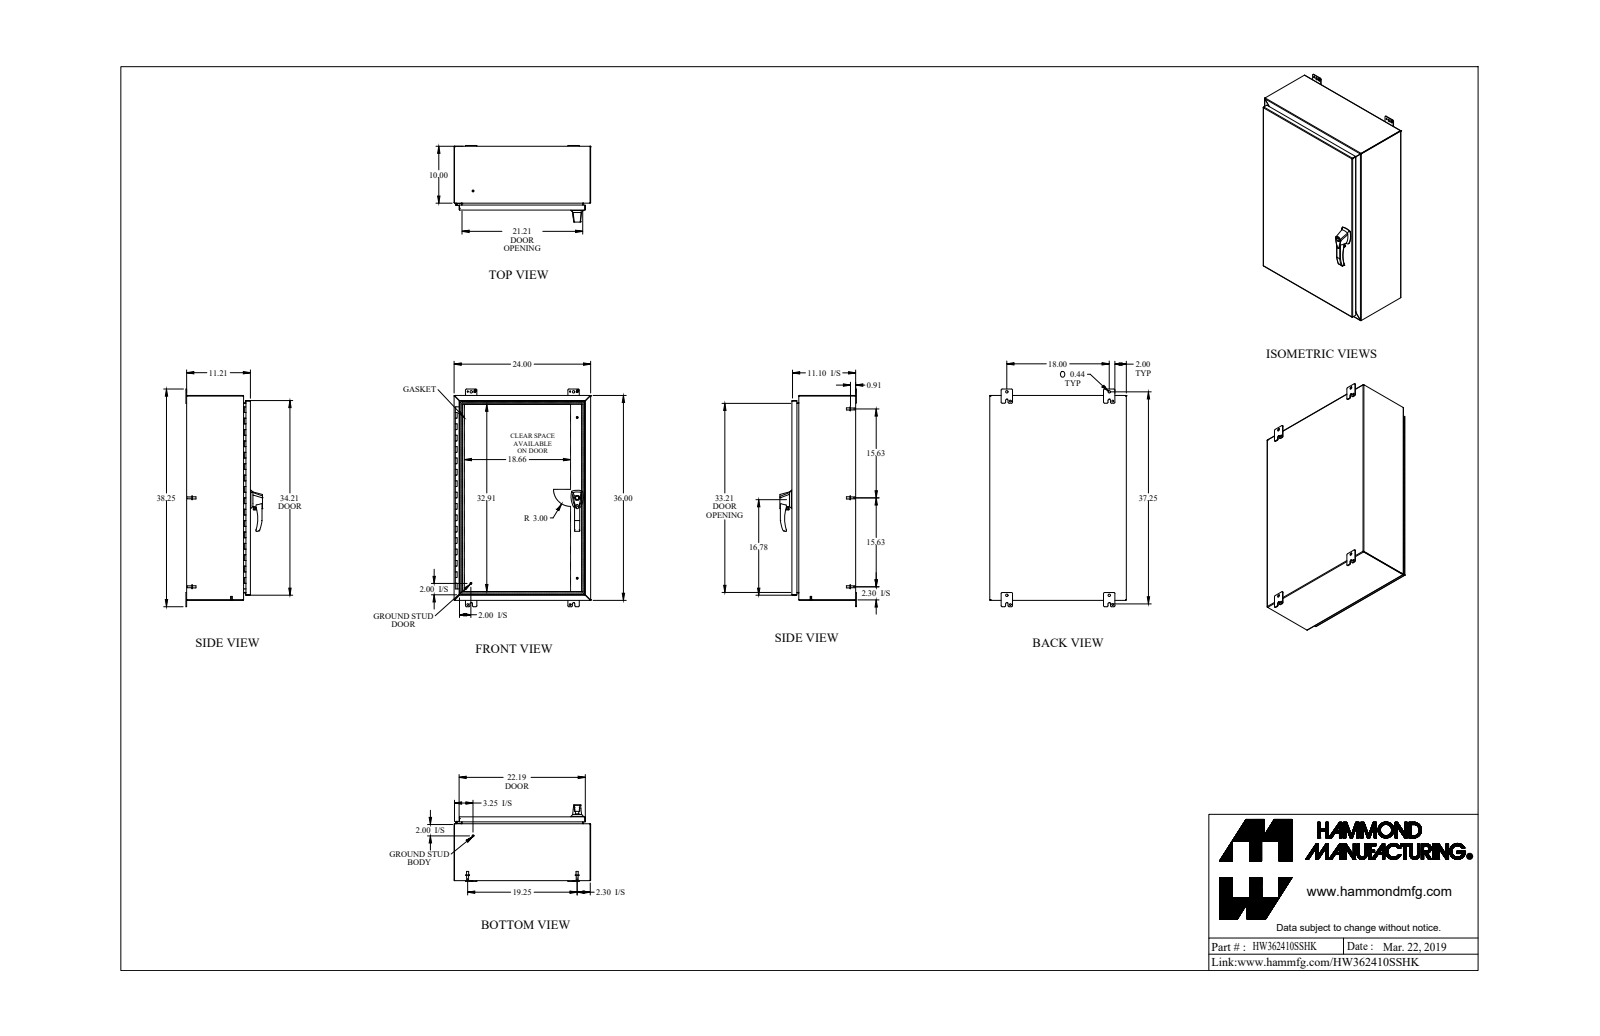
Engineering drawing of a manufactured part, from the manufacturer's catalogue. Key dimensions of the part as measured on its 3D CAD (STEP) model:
Part name (STEP PRODUCT): HW362410SSHK
STEP written by: SolidWorks 2018 (AUTOMOTIVE_DESIGN)
Units: inches
Bodies: 44 solids, 1544 faces (737 planar, 641 cylindrical, 166 other)
Overall size (bounding box): 38.25 × 24 × 13.45
Volume: 270.1 in³ · Surface area: 7 073 in²
Round holes (diameter × count): ⌀0.176 ×6, ⌀0.313 ×5, ⌀0.25 ×3, ⌀0.265 ×3, ⌀0.413 ×3, ⌀0.196 ×2, ⌀0.256 ×2, ⌀0.394 ×2, ⌀0.437 ×2, ⌀0.187 ×1, ⌀0.233 ×1, ⌀0.33 ×1
Round bosses / shafts (diameter × count): ⌀0.375 ×11, ⌀0.25 ×7, ⌀0.65 ×6, ⌀0.332 ×6, ⌀0.156 ×6, ⌀1 ×3, ⌀0.51 ×3, ⌀0.63 ×2
Partial cylindrical surfaces — rounded edges, fillets, slot ends (radius × count): R0.25 ×27, R0.188 ×23, R0.036 ×20, R0.108 ×20, R0.06 ×12, R0.125 ×9, R0.045 ×8, R0.218 ×8
Main face-to-face distances: 0.072, 11.138, 11.066, 0.072, 11.138, 11.21, 23.928, 35.928, 23.856, 24
Hole centre spacings: 1.11, 14.118, 14.119, 28.237, 10.37, 14.119, 18, 37.38
